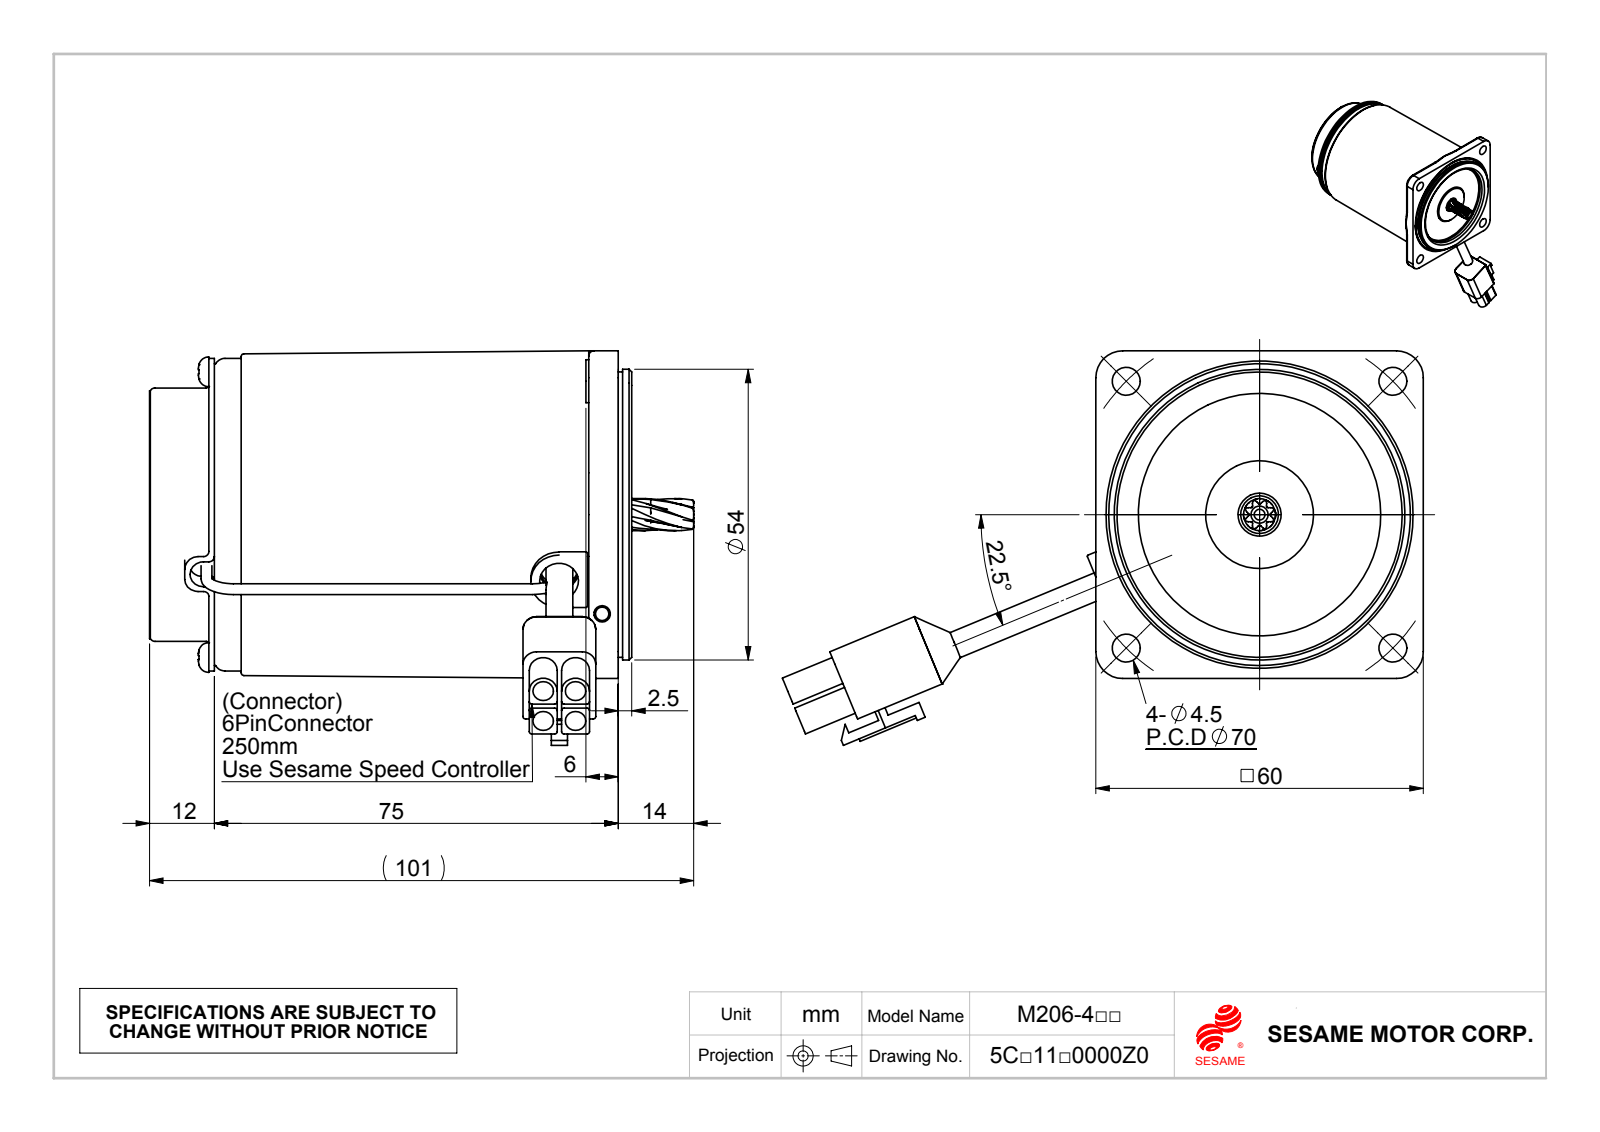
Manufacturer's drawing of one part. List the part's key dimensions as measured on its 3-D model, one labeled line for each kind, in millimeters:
Part name (STEP PRODUCT): 06GN_0成品; C254_Default; M206-RK-R_Default; 線扣 (+1 more)
STEP written by: SolidWorks 2010 (CONFIG_CONTROL_DESIGN)
Units: millimetres
Bodies: 9 solids, 563 faces (164 planar, 205 cylindrical, 194 other)
Overall size (bounding box): 118.98 × 101 × 73.2
Volume: 80 897 mm³ · Surface area: 55 869 mm²
Round holes (diameter × count): ⌀2.5 ×5, ⌀3.2 ×4, ⌀3.8 ×4, ⌀5.2 ×4, ⌀5.5 ×4, ⌀2 ×2, ⌀2.6 ×2, ⌀3.1 ×2, ⌀7 ×1, ⌀7.2 ×1, ⌀9.5 ×1, ⌀15 ×1
Round bosses / shafts (diameter × count): ⌀8 ×4, ⌀5.5 ×2, ⌀3 ×2, ⌀2 ×2, ⌀58 ×1, ⌀53.93 ×1, ⌀52.93 ×1, ⌀47 ×1
Partial cylindrical surfaces — rounded edges, fillets, slot ends (radius × count): R0.5 ×14, R1 ×10, R0.25 ×8, R0.3 ×8, R2.5 ×7, R5 ×4, R1.3 ×2, R2.6 ×2
Main face-to-face distances: 74.5, 73.5, 1, 3, 70.5, 12, 85.5, 4, 75, 15
Hole centre spacings: 37.08, 6, 12.25, 4.24, 9.28, 9.37, 17.15, 17.32
